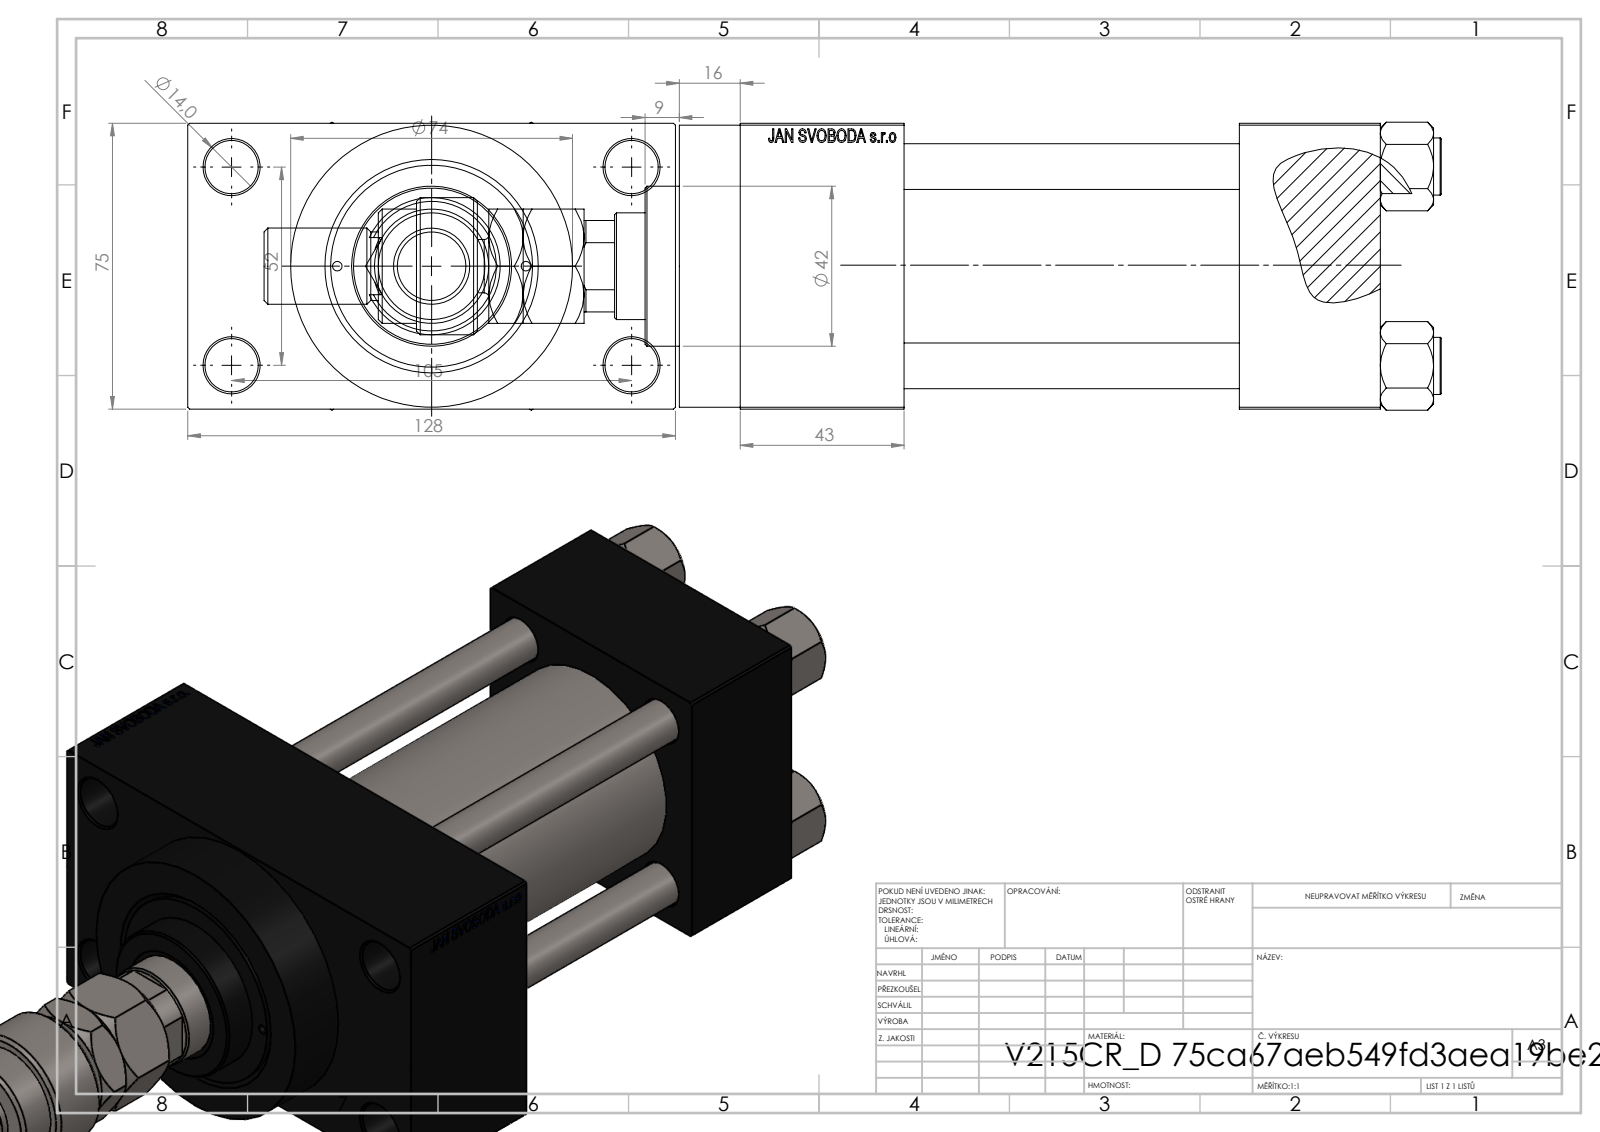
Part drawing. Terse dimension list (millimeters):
name: NUT_M5_D; V215CR_VCP_D; V215CR_D_Body; V215_VC_A (+3 more)
written by: SolidWorks 2019 (CONFIG_CONTROL_DESIGN)
unit: mm
bodies: 13 solids, 1196 faces (527 planar, 105 cylindrical, 564 other)
size: 309 × 128 × 75.54
volume: 901 918 mm³; area: 200 939 mm²
holes: 4× ⌀12, 4× ⌀14, 2× ⌀2.5, 2× ⌀7, 2× ⌀20.96, 2× ⌀30, 1× ⌀18.5, 1× ⌀28, 1× ⌀31, 1× ⌀41, 1× ⌀50, 1× ⌀53
bosses: 4× ⌀15, 1× ⌀74, 1× ⌀56, 1× ⌀42, 1× ⌀36, 1× ⌀30, 1× ⌀22, 1× ⌀20
rounds: 1× R7.5, 1× R12, 1× R13.5
face distances: 75, 88, 125, 37, 26.5, 168, 43, 131, 101.5, 16
hole spacings: 26.19, 26.35, 36.98, 38.03, 52.3, 57.22, 58.43, 58.59
